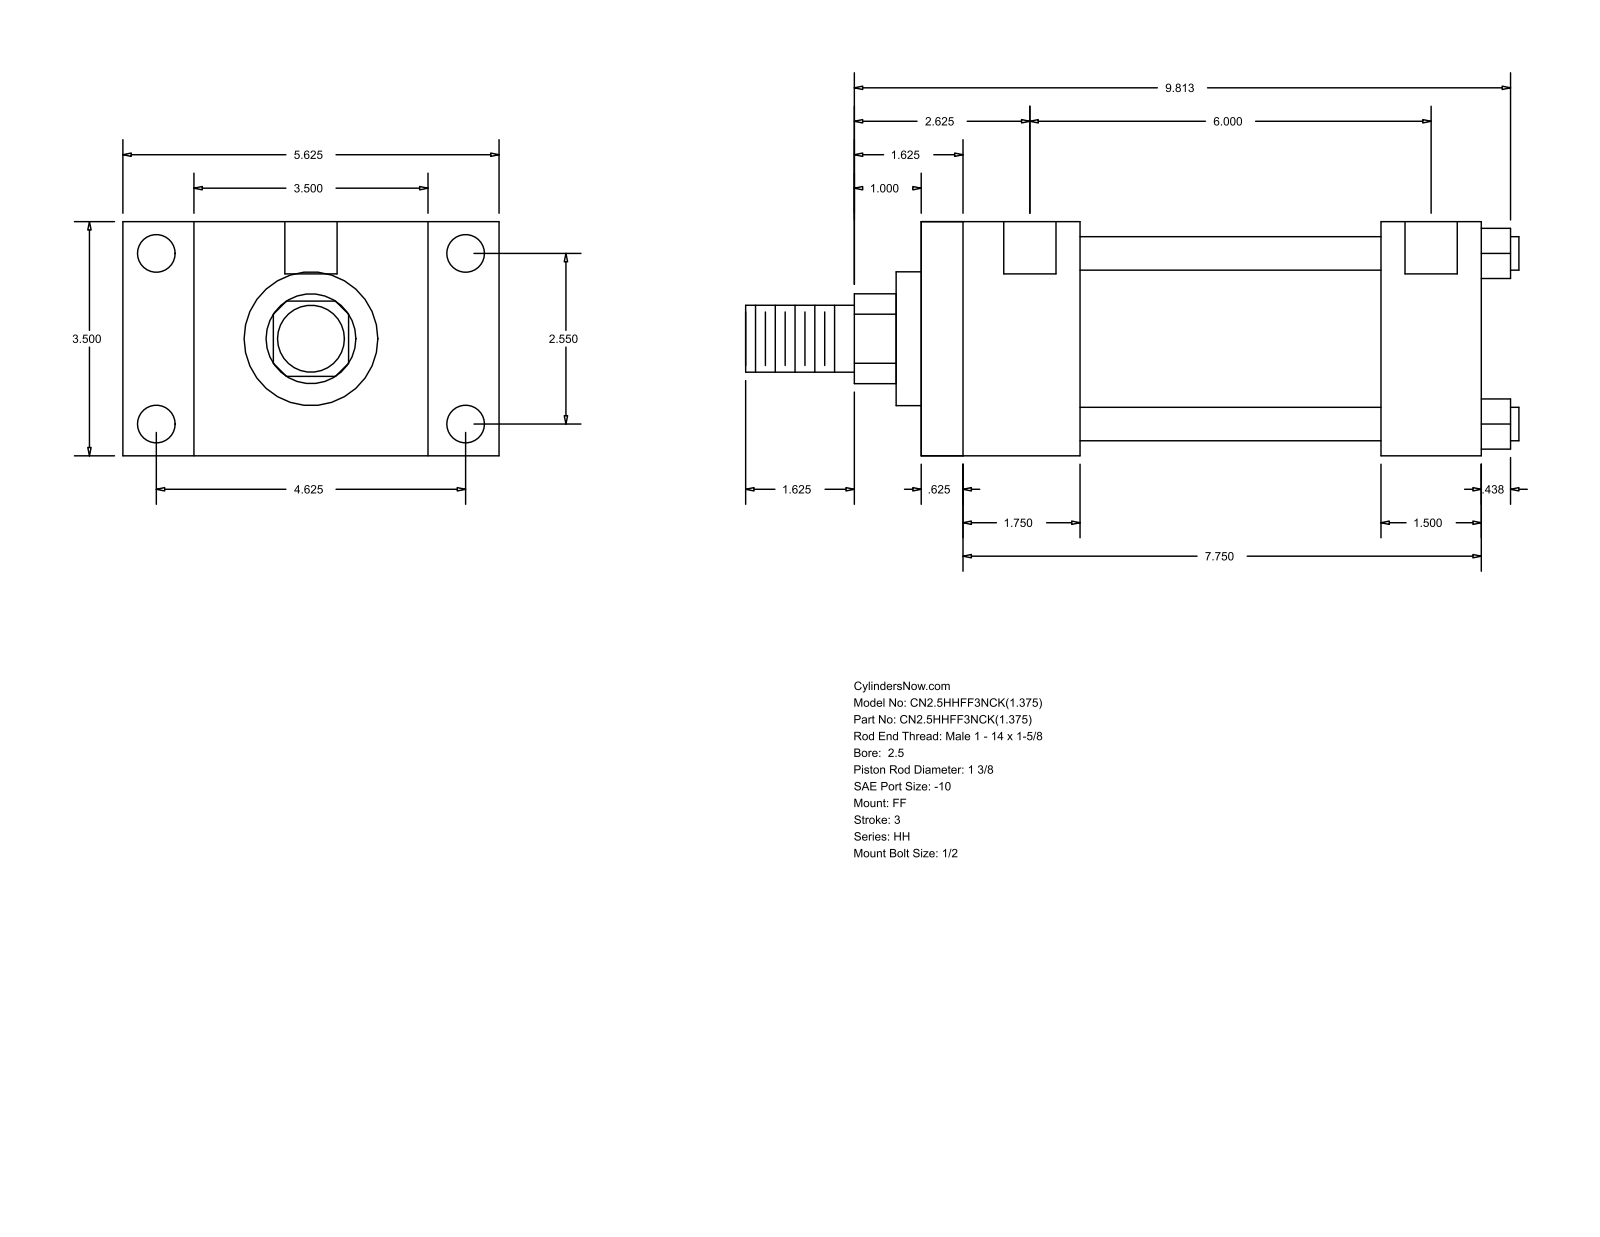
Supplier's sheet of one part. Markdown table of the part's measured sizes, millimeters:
| quantity | value |
| --- | --- |
| part name | HH_FF__0250_1.375 |
| STEP written by | GSSL Pune (CONFIG_CONTROL_DESIGN) |
| units | millimeters |
| bodies | 0 solids, 92 faces (64 planar, 28 cylindrical, 0 other) |
| overall size | 293.69 × 142.88 × 88.9 |
| round holes (diameter × count) | 5.56 × 4, 14.3 × 4, 19.84 × 2 |
| round bosses / shafts (diameter × count) | 12.7 × 4, 73.03 × 1, 50.8 × 1, 34.92 × 1, 25.4 × 1 |
| partial cylindrical surfaces (radius × count) | 17.06 × 1 |
| main face-to-face distances | 88.9, 212.72, 15.87, 196.85, 60.32, 44.45, 152.4, 174.63, 158.76, 114.31 |
| hole center spacings | 64.76, 117.48, 134.15, 155.57, 1.58, 1.59, 152.4, 153.98 |
